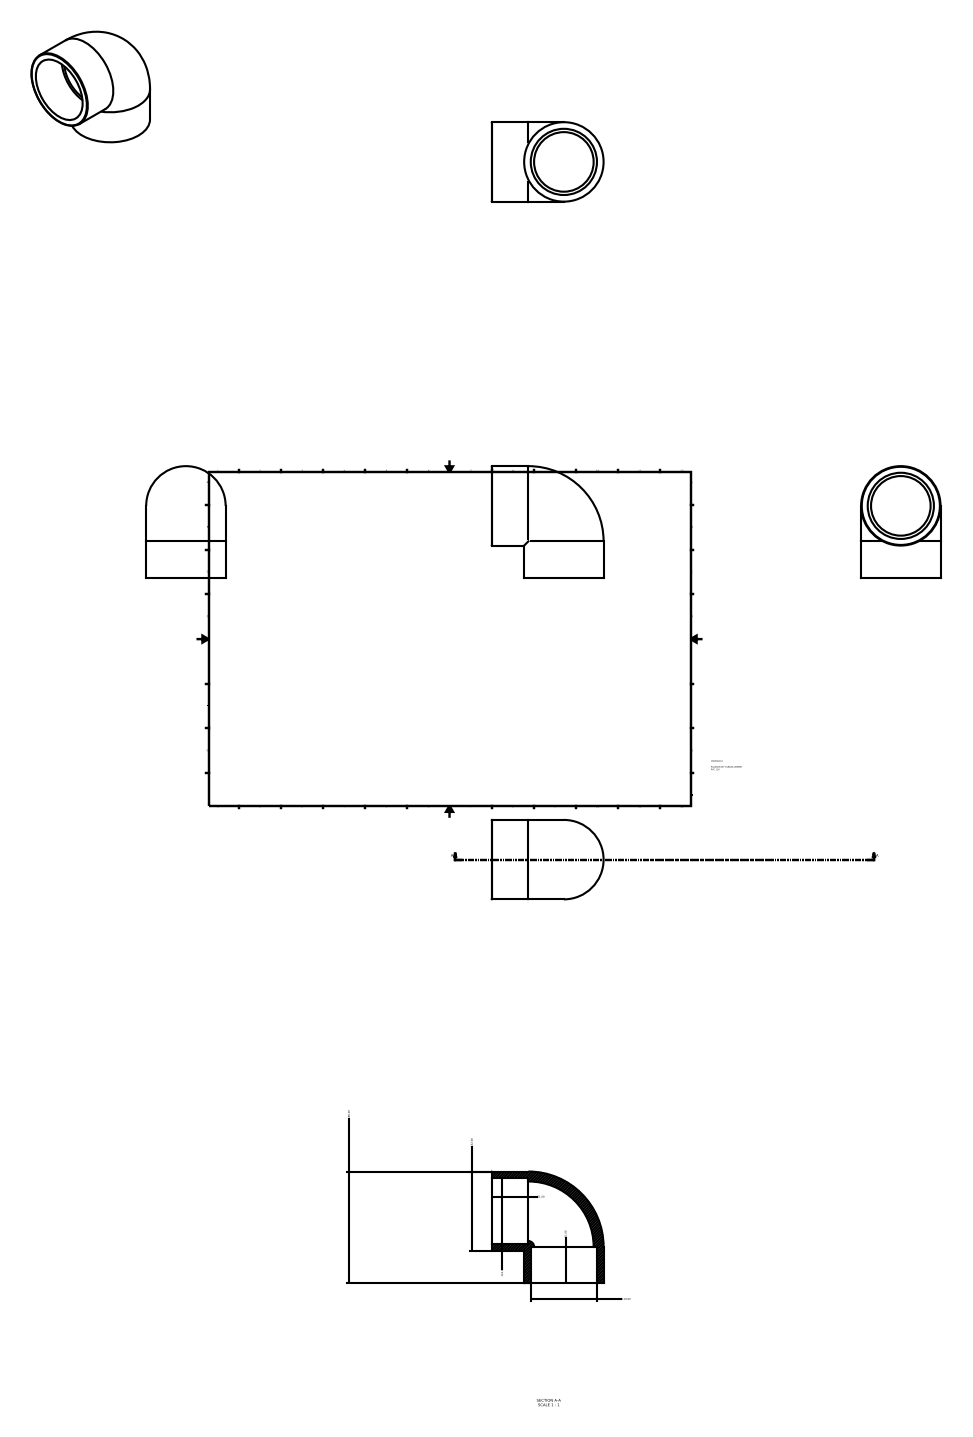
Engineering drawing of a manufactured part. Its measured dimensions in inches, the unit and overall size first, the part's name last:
Units: inches
Overall size (bounding box): 7.323 × 7.323 × 5.197
Round holes (diameter × count): ⌀4.331 ×2
Round bosses / shafts (diameter × count): ⌀5.197 ×2
Main face-to-face distances: 2.402
Volume: 65.78 in³ · Surface area: 266.2 in²
Bodies: 1 solid, 11 faces (4 planar, 4 cylindrical, 3 other)
Part name (STEP PRODUCT): 050500110
STEP written by: Autodesk Inventor 2015 (AUTOMOTIVE_DESIGN)
